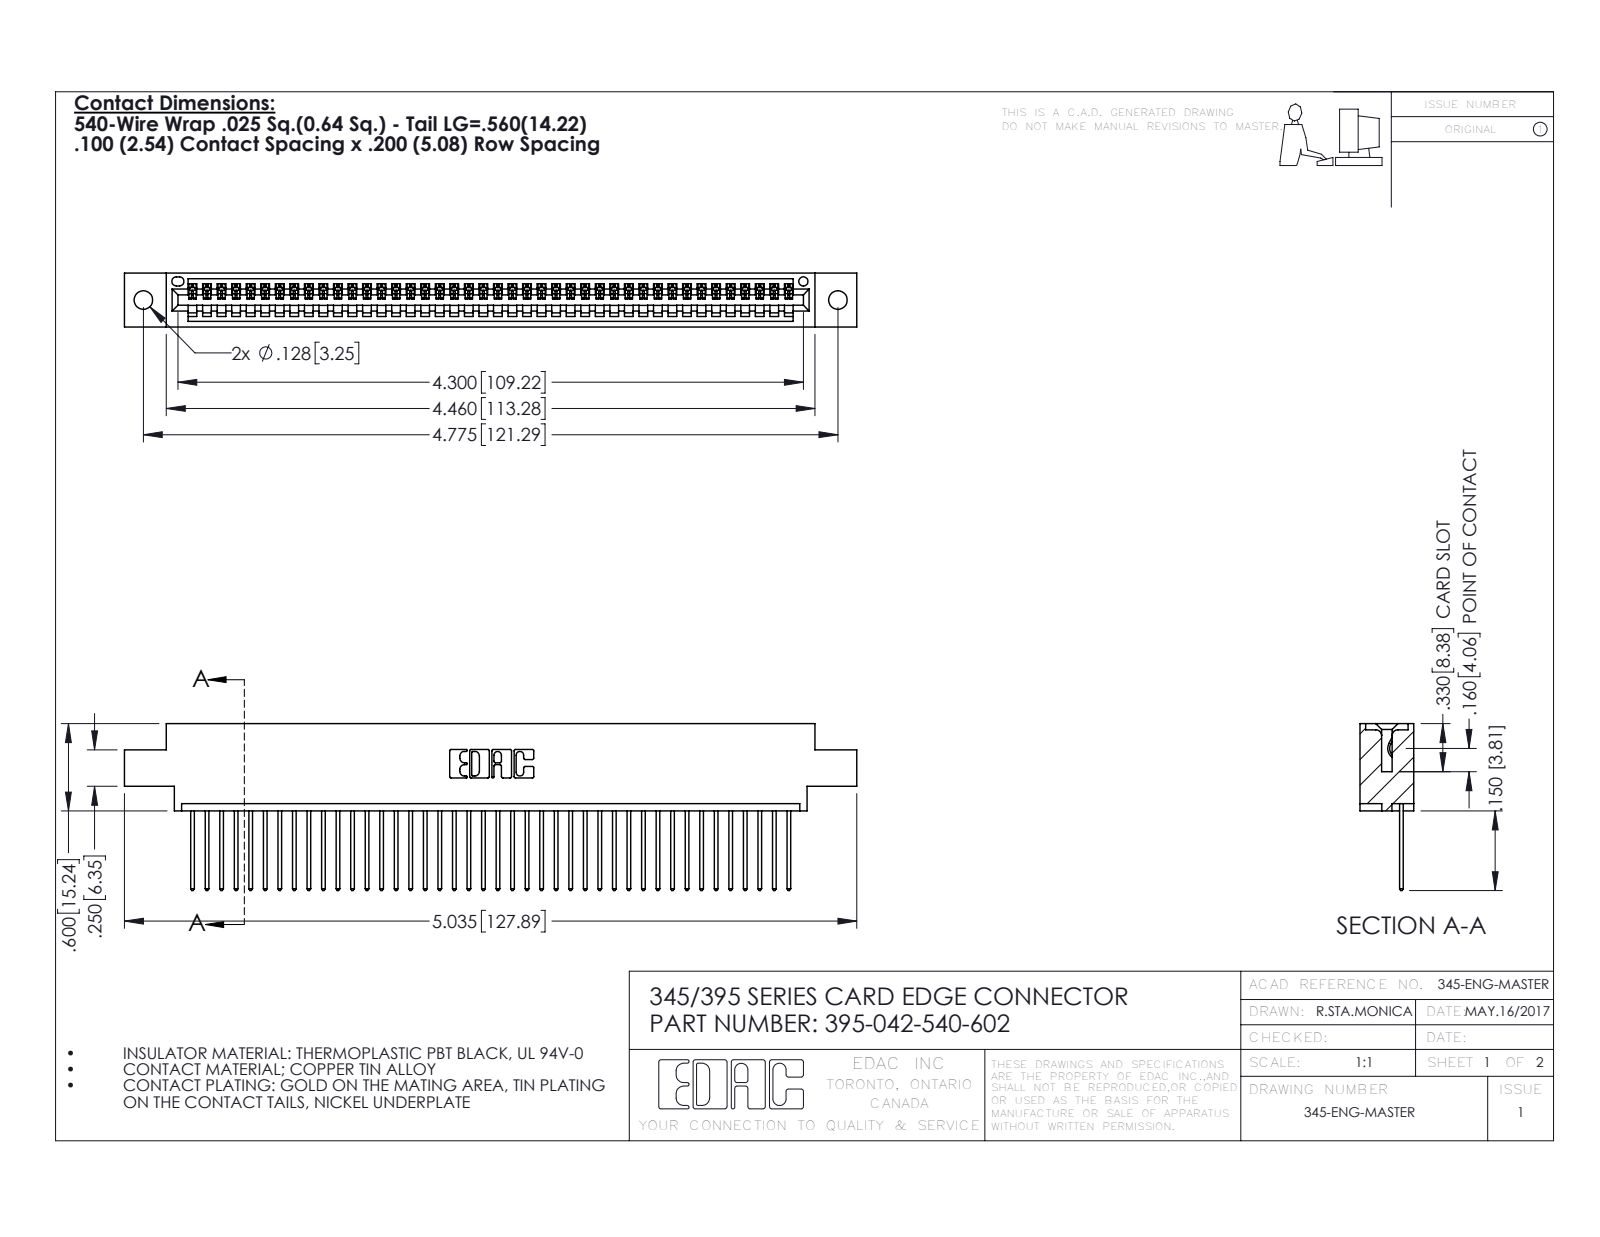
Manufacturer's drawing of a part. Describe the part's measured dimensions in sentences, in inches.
The part is named "345-292-001_345-293-140; 345 Part_0.170 Offset - 0.128 Dia; 395-042-540-602". Its 3-D file was written by "SolidWorks 2016 (CONFIG_CONTROL_DESIGN)". It is 43 solids with 2566 faces: 1764 planar, 802 cylindrical and 0 other. Overall it measures 5.035 by 1.147 by 0.37 inches. Its volume is 0.736 cubic inches and its surface area 25.24 square inches. Round holes: 2 of diameter 0.128, 1 of diameter 0.064. Partial cylindrical surfaces (rounded edges, fillets, slot ends): 84 of radius 0.006, 84 of radius 0.01, 22 of radius 0.01, 6 of radius 0.007, 6 of radius 0.031, 3 of radius 0.026, 2 of radius 0.031, 2 of radius 0.04. The main face-to-face distances are 0.072, 0.298, 0.37, 0.098, 0.272, 0.025, 0.2, 0.225, 0.175, 0.149. The hole center spacings are 0.27, 4.539, 4.775.
